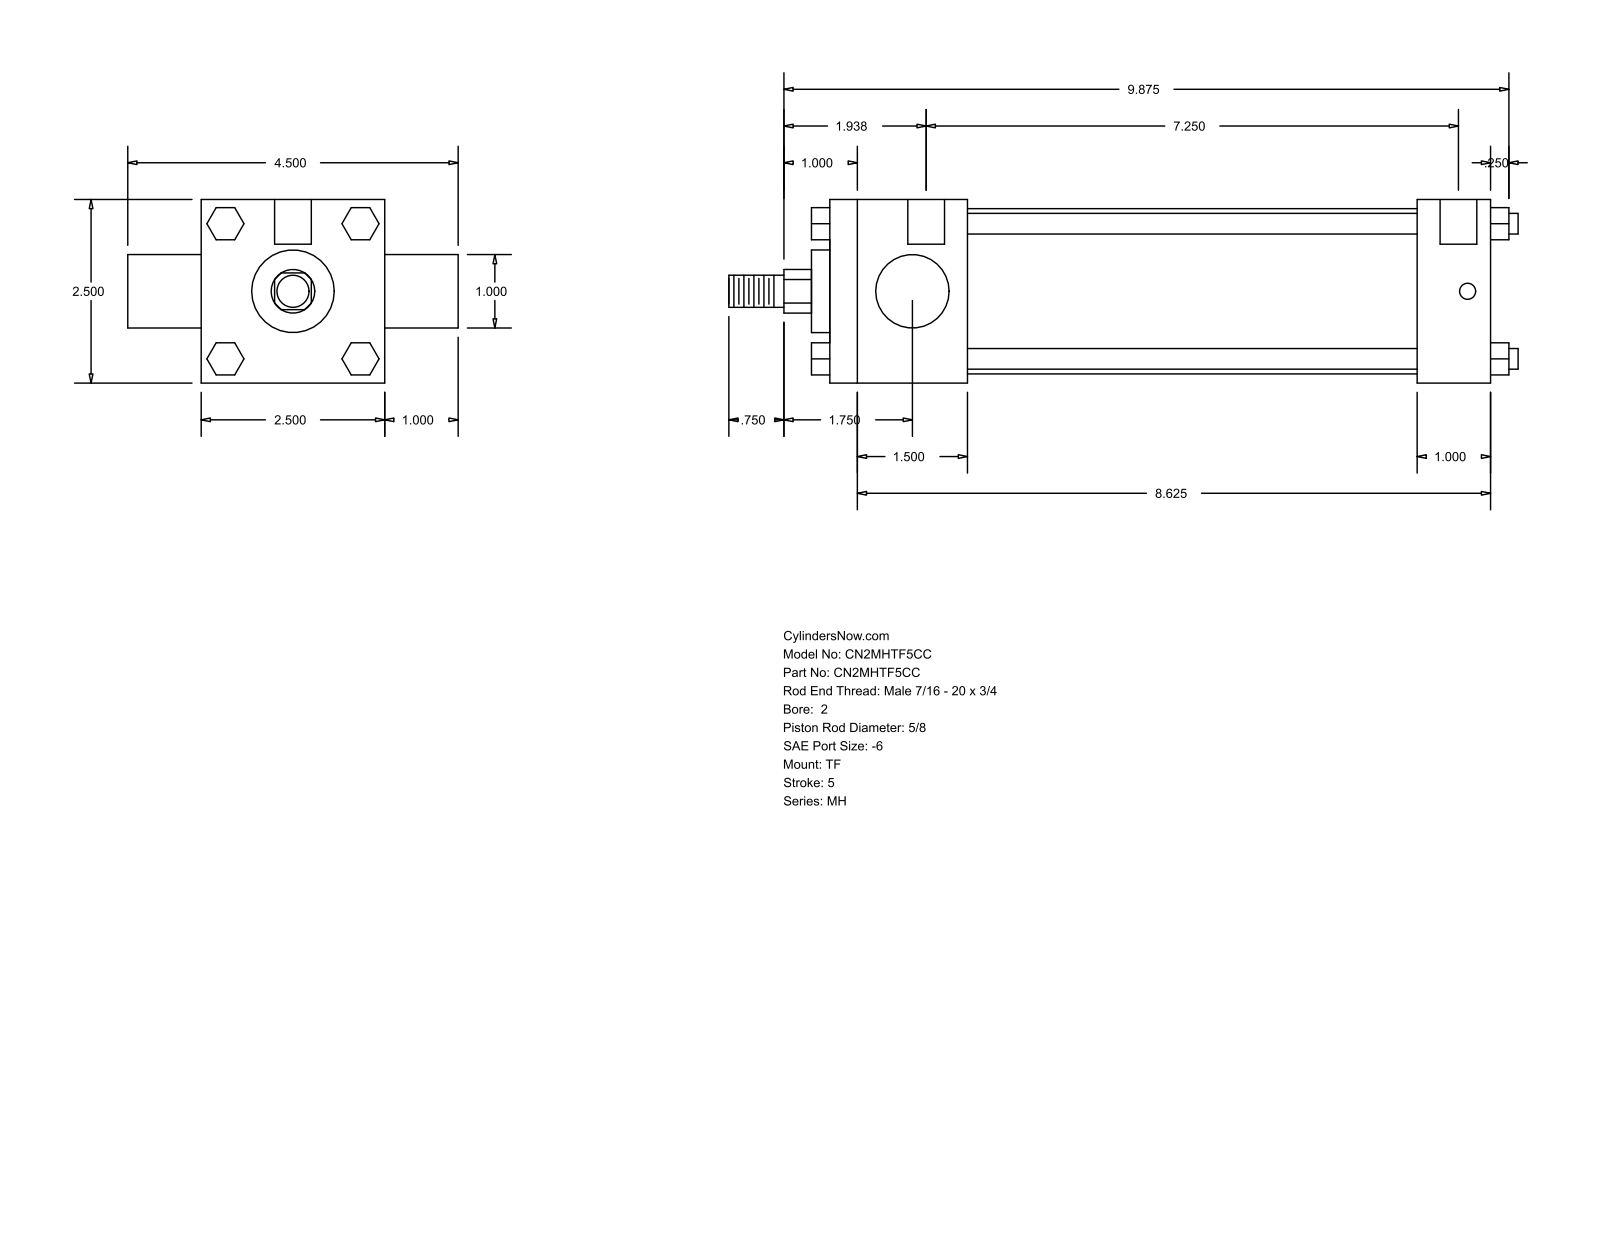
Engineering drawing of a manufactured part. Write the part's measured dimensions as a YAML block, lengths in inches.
part_name: "MH_TF__0200_0.625"
step_written_by: "GSSL Pune (CONFIG_CONTROL_DESIGN)"
units: inches
bodies: {solids: 0, faces: 120, planar: 92, cylindrical: 28, other: 0}
overall_size: [10.75, 4.5, 2.5]
round_holes:
  - {diameter: 0.219, count: 3}
  - {diameter: 0.5, count: 2}
round_bosses_or_shafts:
  - {diameter: 0.281, count: 4}
  - {diameter: 2.25, count: 1}
  - {diameter: 1.125, count: 1}
  - {diameter: 1, count: 1}
  - {diameter: 0.625, count: 1}
  - {diameter: 0.437, count: 1}
partial_cylinders:
  - {radius: 0.297, count: 1}
face_to_face_distances: [2.5, 9, 1, 1.875, 8, 6.125, 7.125, 0.25, 3.5, 9.25]
hole_center_spacings: [0.125, 0.187, 7.25, 7.375, 7.437, 7.563]
